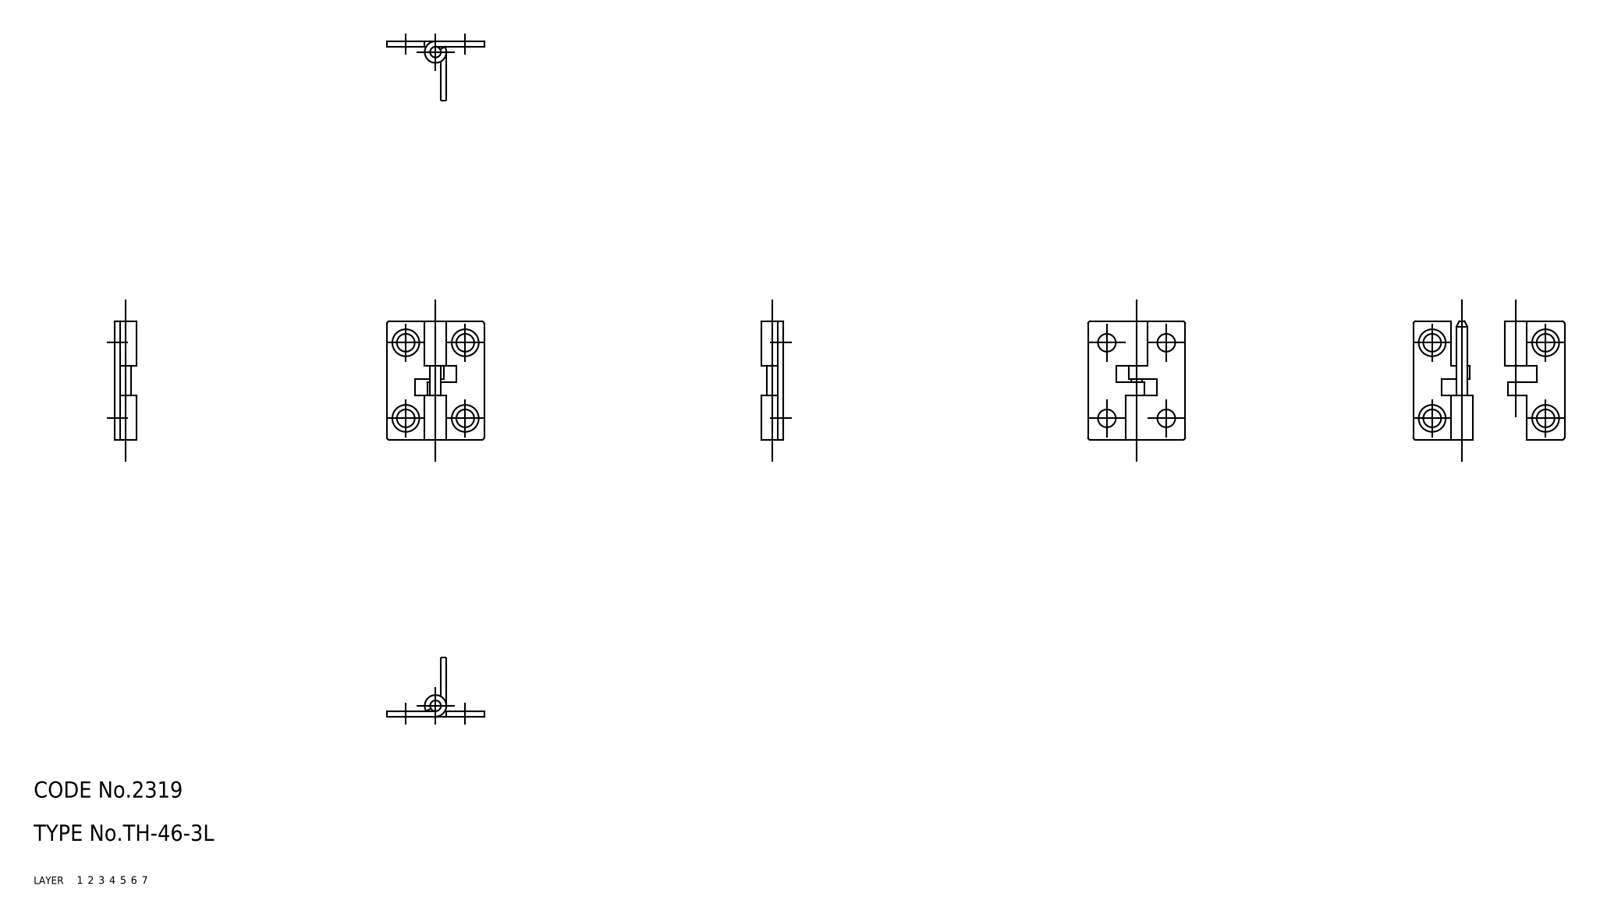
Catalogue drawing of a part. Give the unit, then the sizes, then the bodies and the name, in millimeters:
Units: millimetres
Overall size (bounding box): 22 × 18 × 4
Volume: 491 mm³ · Surface area: 1 223 mm²
Bodies: 3 solids, 54 faces (0 planar, 0 cylindrical, 54 other)
Part name (STEP PRODUCT): shaft; hinge piece_B; hinge piece_A; TH_46_3L_9653_36
STEP written by: CADfix (AUTOMOTIVE_DESIGN)
